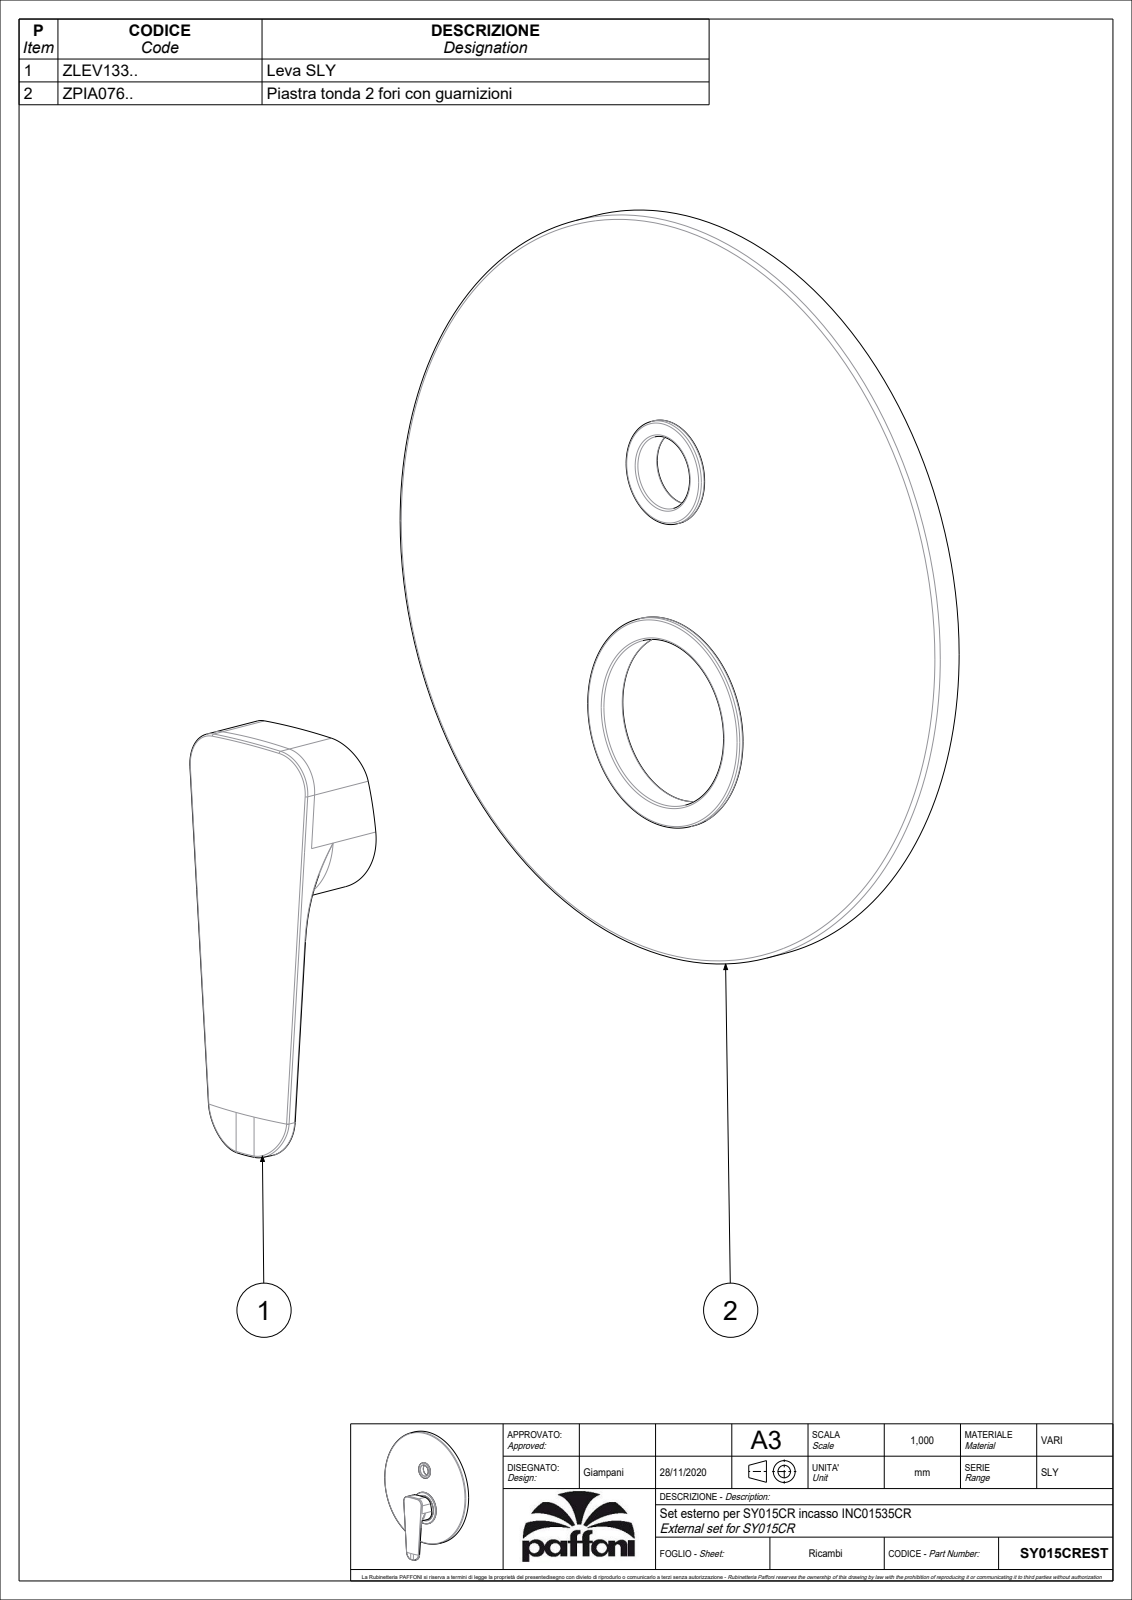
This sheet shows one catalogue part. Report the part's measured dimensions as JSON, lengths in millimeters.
{"part_name": "SY015CREST", "step_written_by": "CREO PARAMETRIC BY PTC INC, 2020044 (CONFIG_CONTROL_DESIGN)", "units": "millimeters", "bodies": {"solids": 2, "faces": 198, "planar": 54, "cylindrical": 58, "other": 86}, "overall_size": [223.98, 200, 41], "volume_mm3": 169272, "surface_area_mm2": 96436, "round_holes": [[3, 1], [3.3, 1], [4.5, 1], [19.1, 1], [44.6, 1], [50, 1], [145, 1], [198, 1]], "round_bosses_or_shafts": [[200, 1], [195, 1], [56.2, 1], [49.9, 1], [25.1, 1], [23.5, 1], [7.6, 1], [5.5, 1]], "partial_cylinders_radius": [[1.5, 4], [10, 2], [4.5, 1], [20.68, 1], [112.27, 1], [200, 1]], "face_to_face_distances": [1, 8, 9, 36.5, 28.5, 27.5, 2, 3, 11, 25.5], "hole_center_spacings": [32.2, 35.8, 68]}
